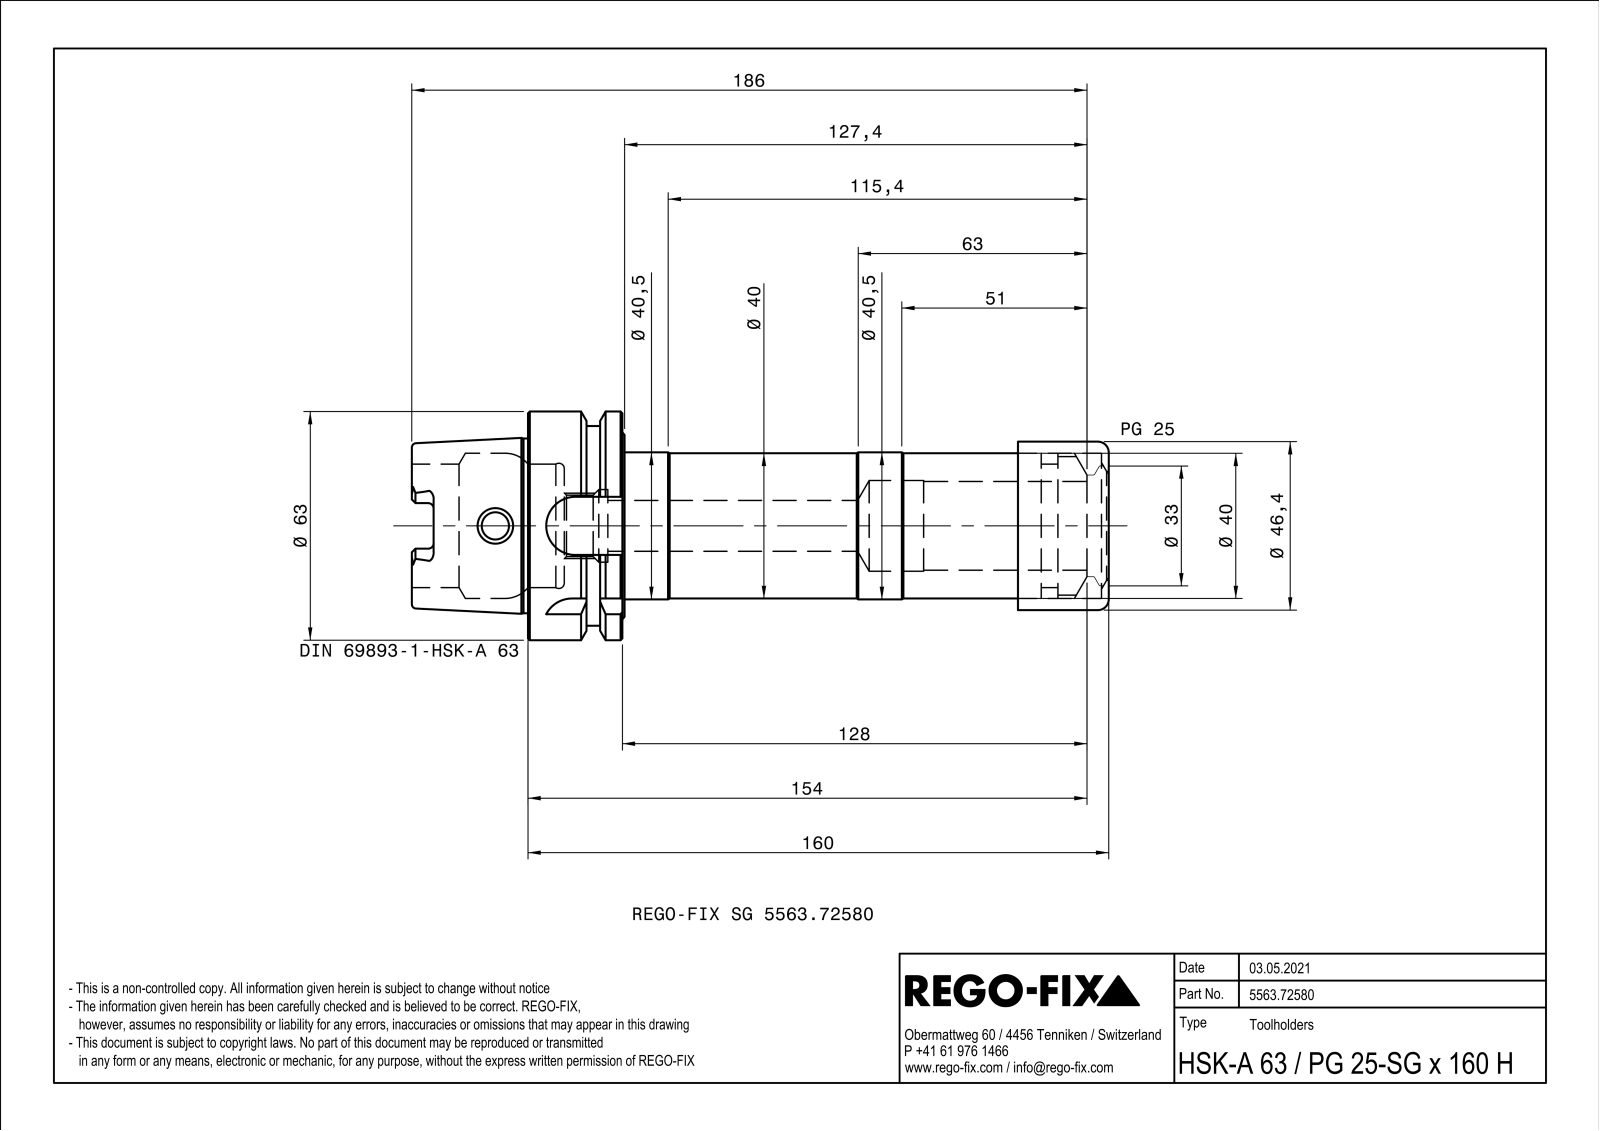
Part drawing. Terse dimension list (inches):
name: 0008430
written by: SIEMENS PLM Software Solid Edge ST10 (AUTOMOTIVE_DESIGN)
unit: in
bodies: 2 solids, 168 faces (55 planar, 47 cylindrical, 66 other)
size: 7.559 × 2.48 × 2.48
volume: 13.01 in³; area: 83.97 in²
holes: 2× ⌀0.295, 1× ⌀0.331, 1× ⌀0.354, 1× ⌀0.394, 1× ⌀0.551, 1× ⌀0.666, 1× ⌀0.787, 1× ⌀0.984, 1× ⌀1.181, 1× ⌀1.339, 1× ⌀1.511, 1× ⌀1.577
bosses: 1× ⌀2.48, 1× ⌀2.165, 1× ⌀1.891, 1× ⌀1.811, 1× ⌀1.594, 1× ⌀1.575
rounds: 6× R0.059, 4× R0.113, 4× R0.315, 1× R0.812, 1× R0.881
face distances: 1.024, 0.654, 0.394, 0.63, 5.276, 6.299, 5.906, 5.252, 0.024, 1.047
hole spacings: 0.866
